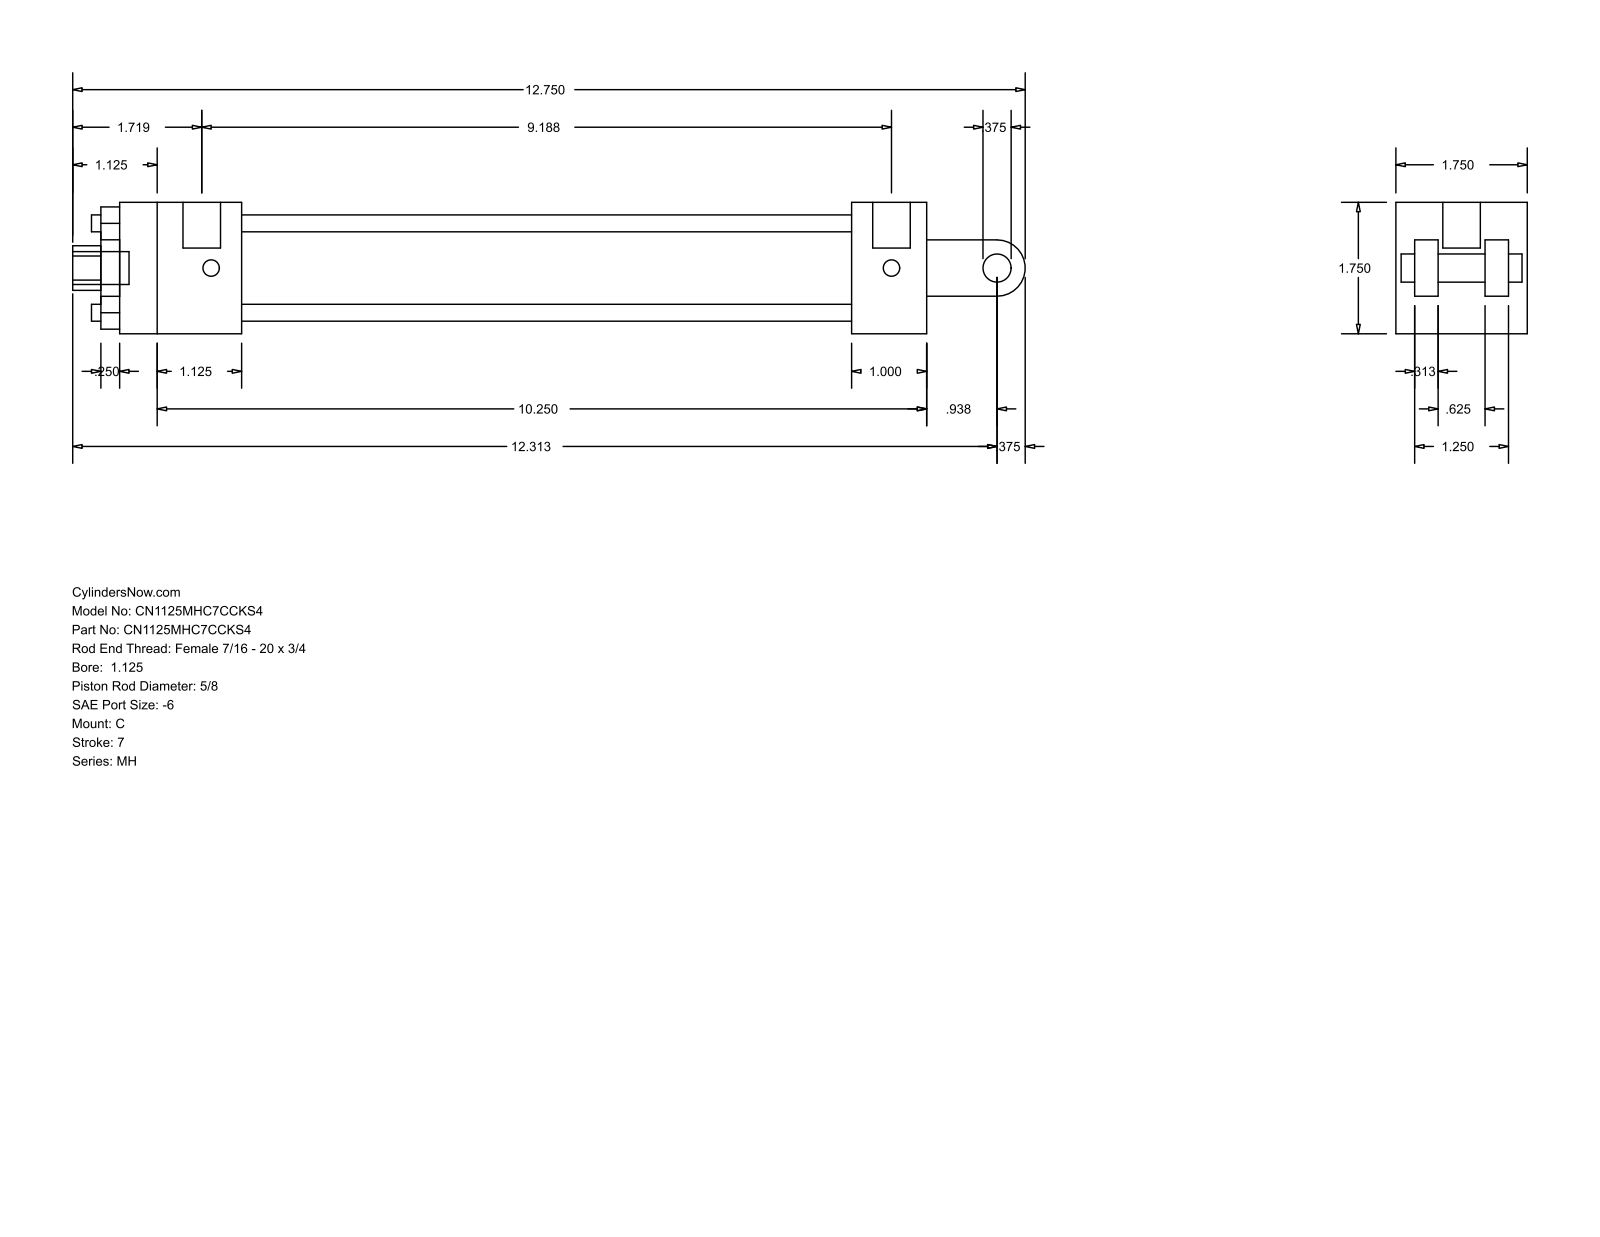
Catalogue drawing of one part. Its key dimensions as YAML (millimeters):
part_name: "MH_C__0112_0.625"
step_written_by: "GSSL Pune (CONFIG_CONTROL_DESIGN)"
units: millimeters
bodies: {solids: 0, faces: 99, planar: 70, cylindrical: 29, other: 0}
overall_size: [322.26, 44.45, 44.45]
round_holes:
  - {diameter: 5.71, count: 4}
  - {diameter: 5.56, count: 2}
  - {diameter: 12.7, count: 1}
  - {diameter: 15.88, count: 1}
  - {diameter: 28.57, count: 1}
  - {diameter: 34.92, count: 1}
round_bosses_or_shafts:
  - {diameter: 5.56, count: 2}
  - {diameter: 12.7, count: 1}
  - {diameter: 11.11, count: 1}
  - {diameter: 9.53, count: 1}
partial_cylinders:
  - {radius: 7.54, count: 1}
  - {radius: 9.53, count: 1}
face_to_face_distances: [44.46, 6.35, 31.76, 14.29, 12.7, 30.17, 38.11, 7.94, 23.82, 41.27]
hole_center_spacings: [21.37, 30.22, 42.74]
